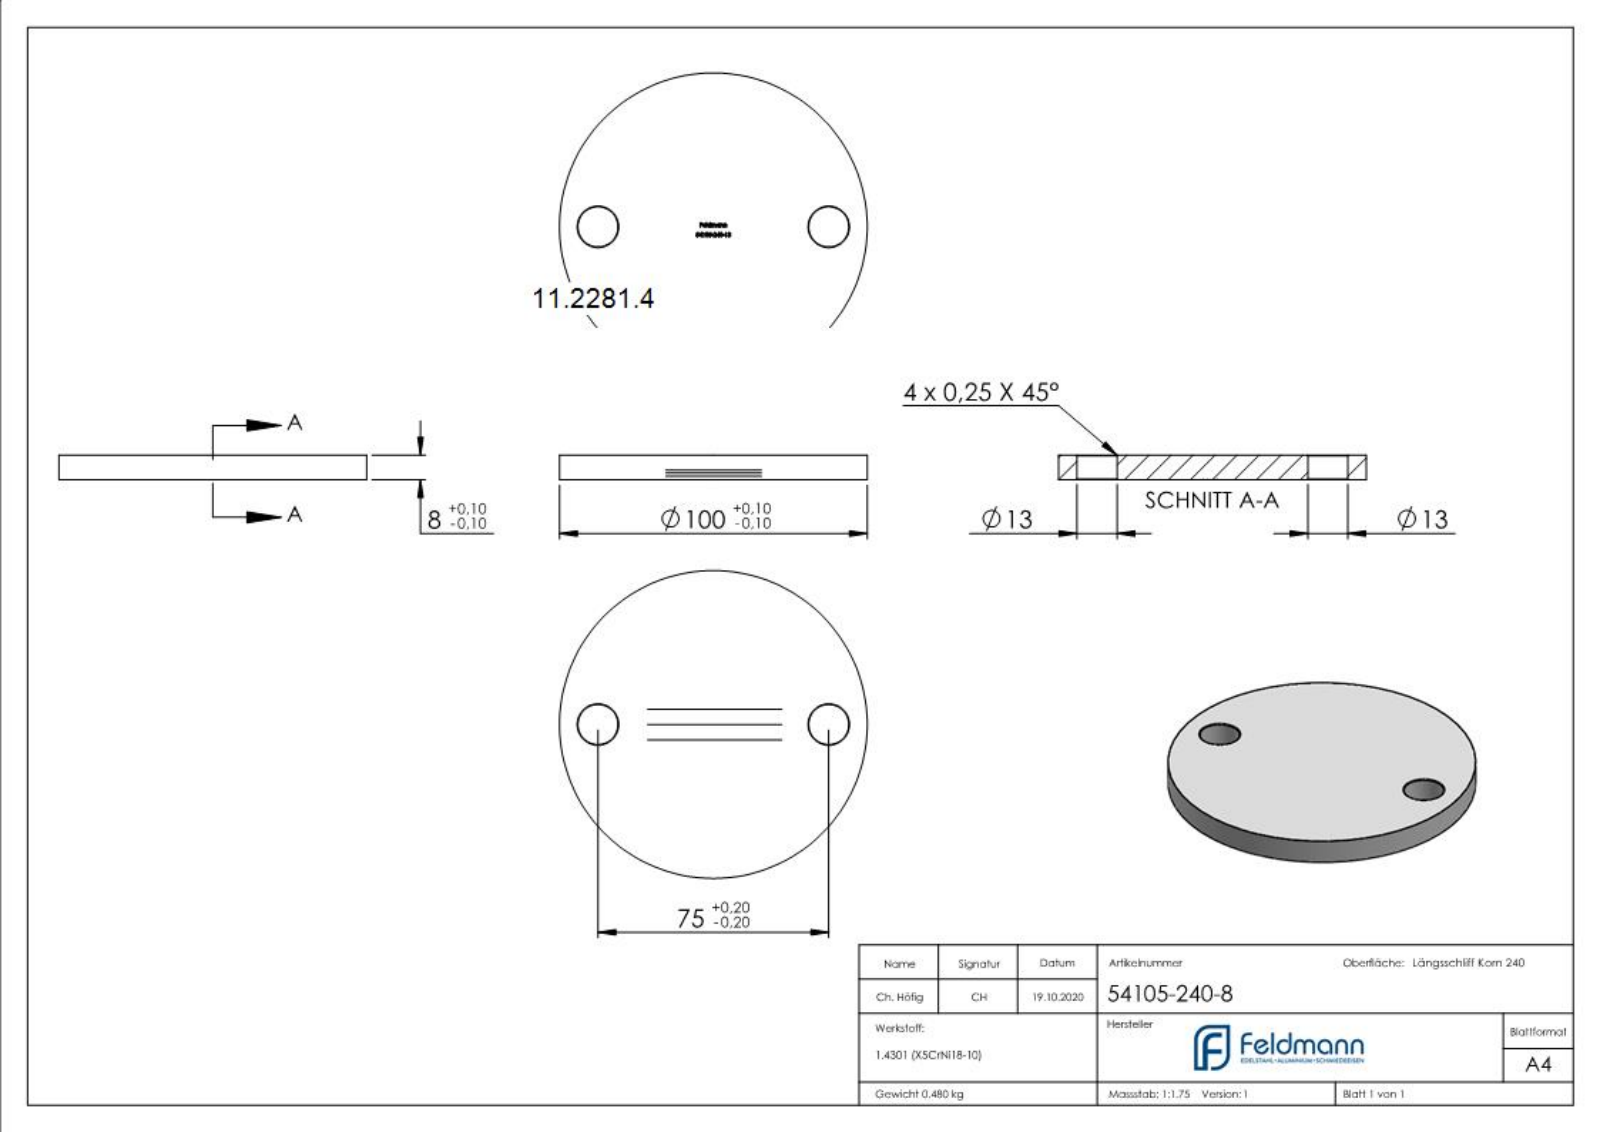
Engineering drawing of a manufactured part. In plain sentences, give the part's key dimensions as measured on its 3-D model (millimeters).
The part is named "54105-240-8". Its 3-D file was written by "SolidWorks 2018 (CONFIG_CONTROL_DESIGN)". It is 1 solid with 261 faces: 142 planar, 6 cylindrical and 113 other. Overall it measures 100 by 100 by 8 millimeters. Its volume is 60 702 cubic millimeters and its surface area 18 331 square millimeters. Round holes: 2 of diameter 13. Round bosses or shafts: 1 of diameter 100. The main face-to-face distances are 8, 7.9, 0.44, 2.97, 3.21, 1.12, 3.19, 0.39, 3.39, 1.19. The hole center spacings are 75.
